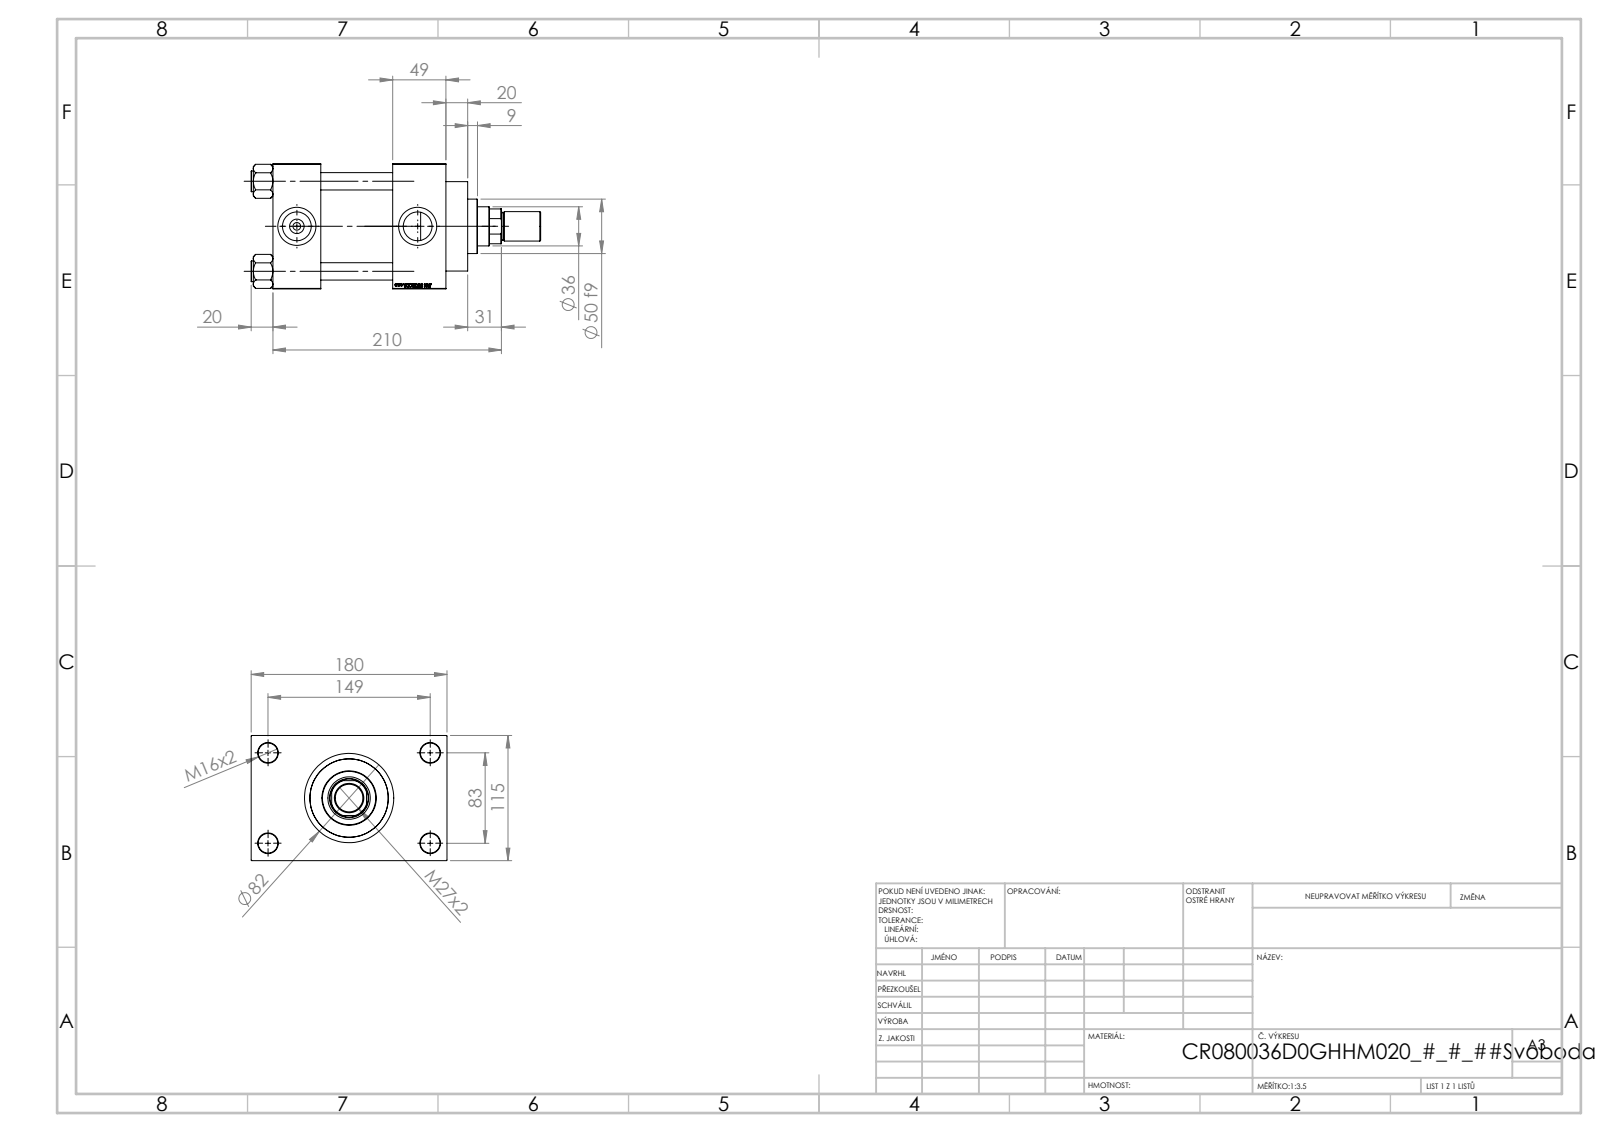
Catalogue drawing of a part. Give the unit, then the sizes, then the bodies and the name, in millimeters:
Units: millimetres
Overall size (bounding box): 266 × 180 × 115
Round holes (diameter × count): ⌀16 ×4, ⌀18 ×4, ⌀7 ×2, ⌀26.44 ×2, ⌀35 ×2, ⌀25.5 ×1, ⌀36 ×1, ⌀39 ×1, ⌀61 ×1, ⌀72 ×1, ⌀80 ×1
Round bosses / shafts (diameter × count): ⌀19 ×4, ⌀86 ×1, ⌀82 ×1, ⌀50 ×1, ⌀27 ×1, ⌀25 ×1
Partial cylindrical surfaces — rounded edges, fillets, slot ends (radius × count): R17.5 ×1
Main face-to-face distances: 115, 66, 110, 49, 44, 159, 32.5, 147.5, 20, 69
Hole centre spacings: 33.15, 58.48, 82.7, 85.28, 89.24, 115.85, 142.43, 83
Volume: 2 000 000 mm³ · Surface area: 300 861 mm²
Bodies: 12 solids, 1165 faces (549 planar, 92 cylindrical, 524 other)
Part name (STEP PRODUCT): V215CR_D_Body; ROD_END_AH; V215_VC_A; V215CR_D_TYCINKA (+2 more)
STEP written by: SolidWorks 2019 (CONFIG_CONTROL_DESIGN)
